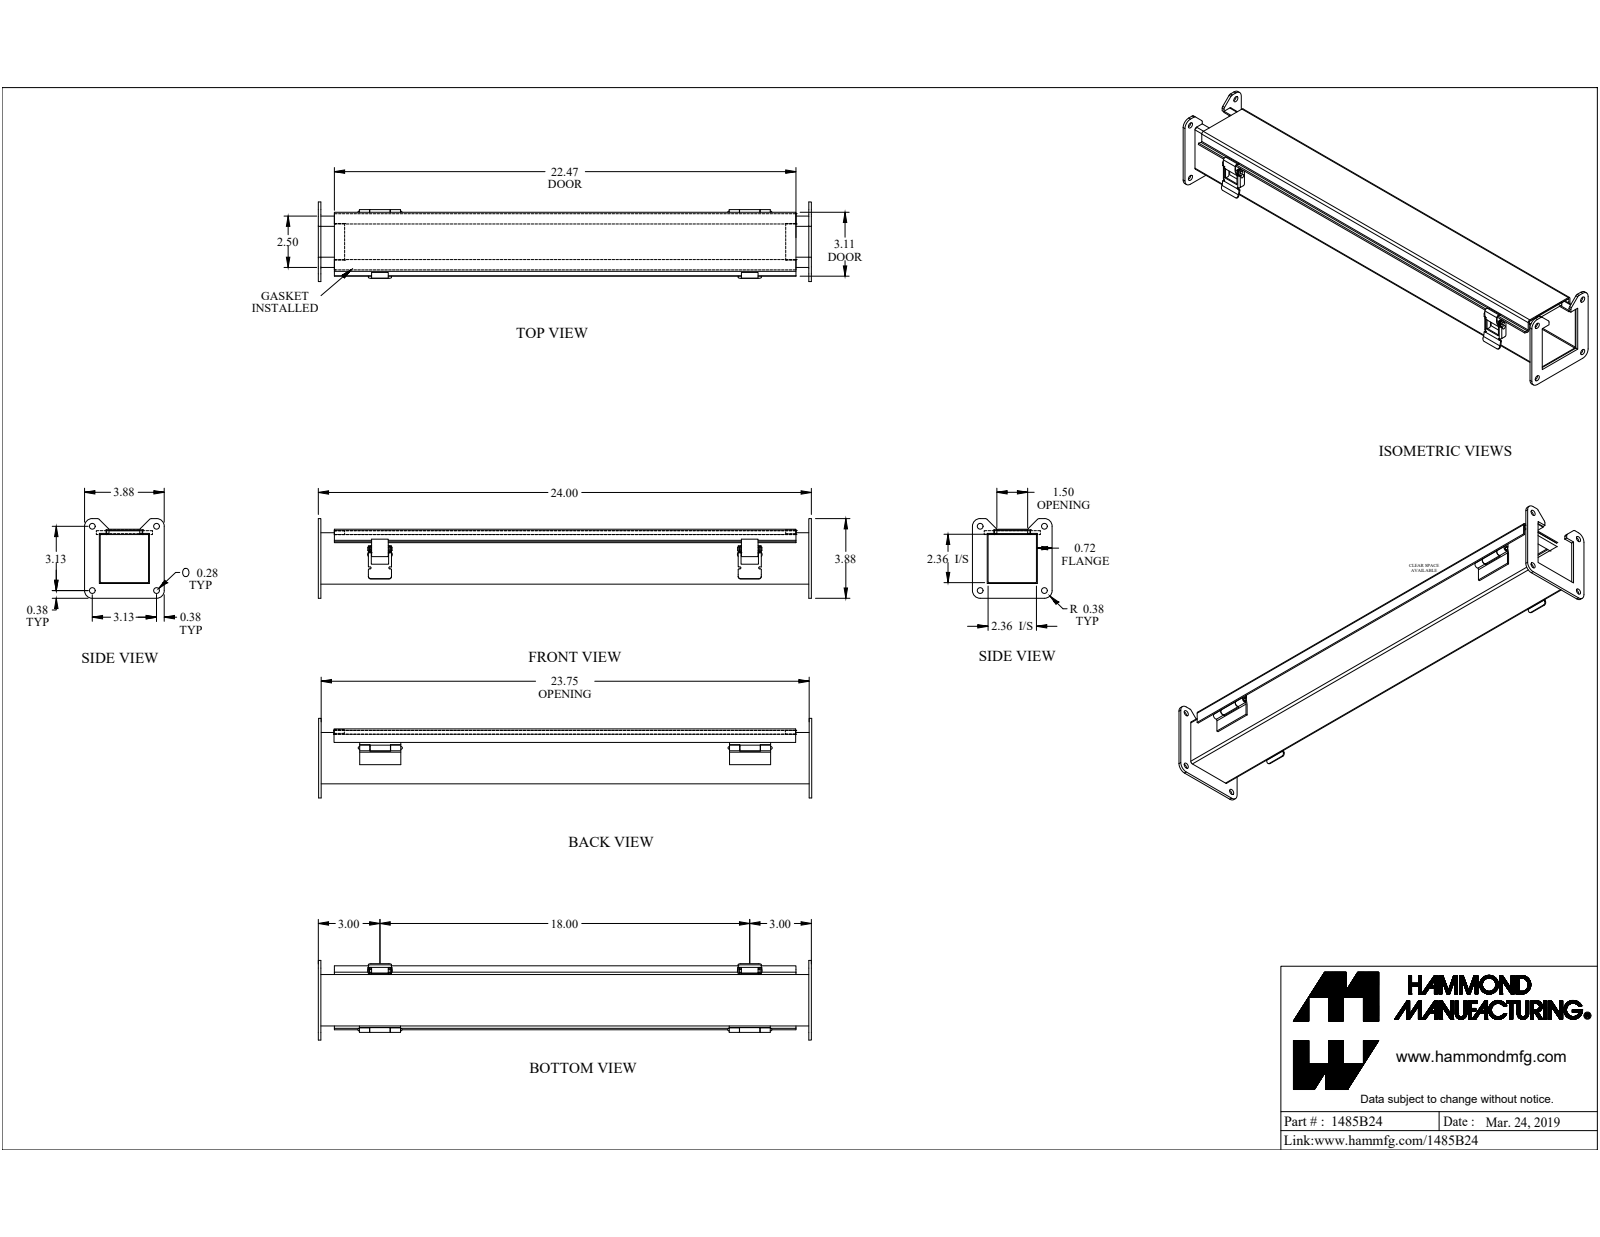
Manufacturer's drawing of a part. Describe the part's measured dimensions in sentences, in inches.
The part is named "1485B24". Its 3-D file was written by "SolidWorks 2019 (CONFIG_CONTROL_DESIGN)". It is 20 solids with 380 faces: 230 planar, 138 cylindrical and 12 other. Overall it measures 24 by 3.875 by 3.875 inches. Its volume is 28.05 cubic inches and its surface area 721.9 square inches. Round holes: 4 of diameter 0.281, 1 of diameter 0.125, 1 of diameter 0.164. Round bosses or shafts: 1 of diameter 0.275, 1 of diameter 0.162, 1 of diameter 0.158, 1 of diameter 0.125, 1 of diameter 0.125. Partial cylindrical surfaces (rounded edges, fillets, slot ends): 9 of radius 0.125, 8 of radius 0.029, 8 of radius 0.086, 7 of radius 0.036, 7 of radius 0.108, 4 of radius 0.015, 4 of radius 0.047, 4 of radius 0.375. The main face-to-face distances are 0.072, 2.428, 2.6, 2.5, 2.356, 2.672, 2.528, 0.172, 2.615, 0.187. The hole center spacings are 3.125, 4.42, 1.075, 1.1, 2.028, 2.063, 2.927, 3.174.
